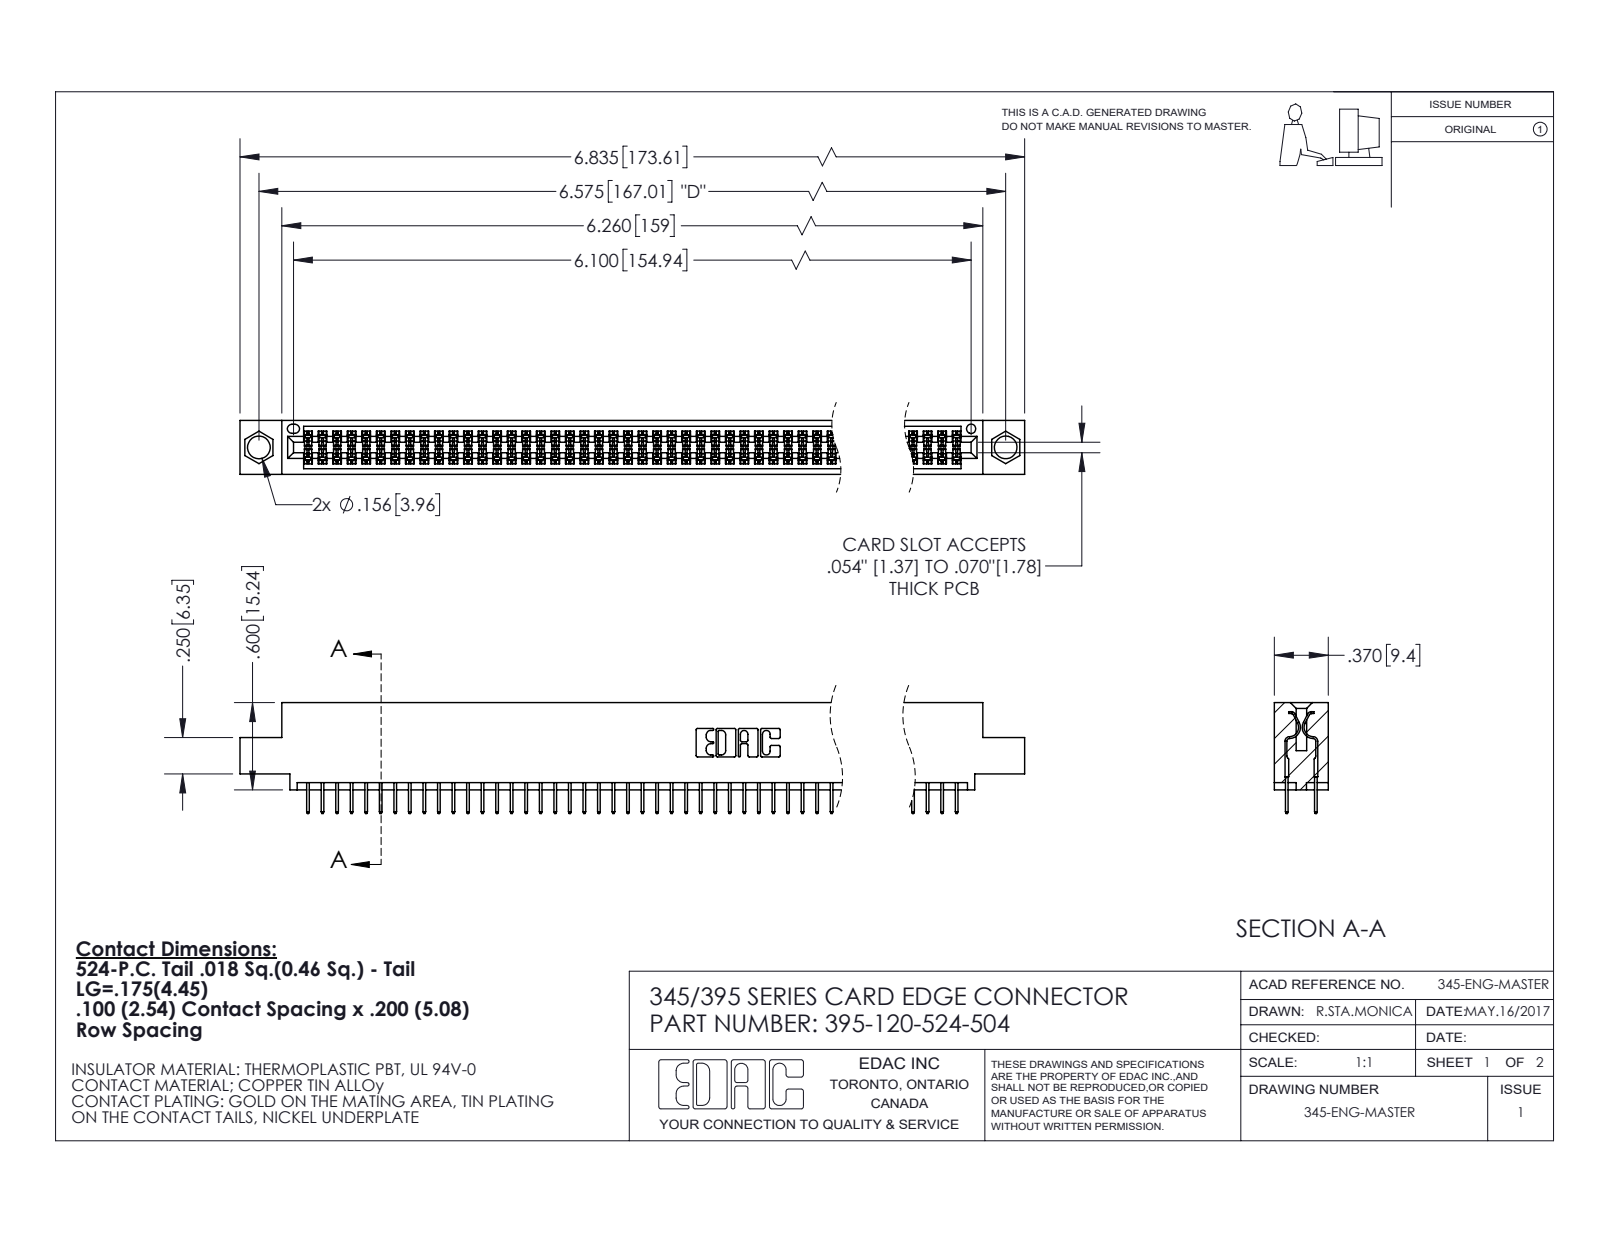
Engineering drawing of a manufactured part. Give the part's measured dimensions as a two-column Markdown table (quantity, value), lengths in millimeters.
| quantity | value |
| --- | --- |
| part name | 345 Part_0.110 Offset - 0.156 Dia-TI; 345-292-001_345-293-124; 395-120-524-504 |
| STEP written by | SolidWorks 2020 (CONFIG_CONTROL_DESIGN) |
| units | millimeters |
| bodies | 121 solids, 6624 faces (4778 planar, 1846 cylindrical, 0 other) |
| overall size | 173.6 × 19.4 × 9.4 |
| volume | 16 670 mm³ |
| surface area | 24 460 mm² |
| round holes (diameter × count) | 4 × 2, 1.6 × 1 |
| partial cylindrical surfaces (radius × count) | 0.2 × 240, 0.3 × 22, 0.2 × 6, 0.8 × 6, 0.7 × 3, 0.4 × 2, 0.5 × 2, 0.6 × 2 |
| main face-to-face distances | 1.8, 7.6, 5.1, 9.4, 2.5, 6.9, 0.6, 5.7, 1.8, 4.4 |
| hole center spacings | 6.9, 161, 167 |
